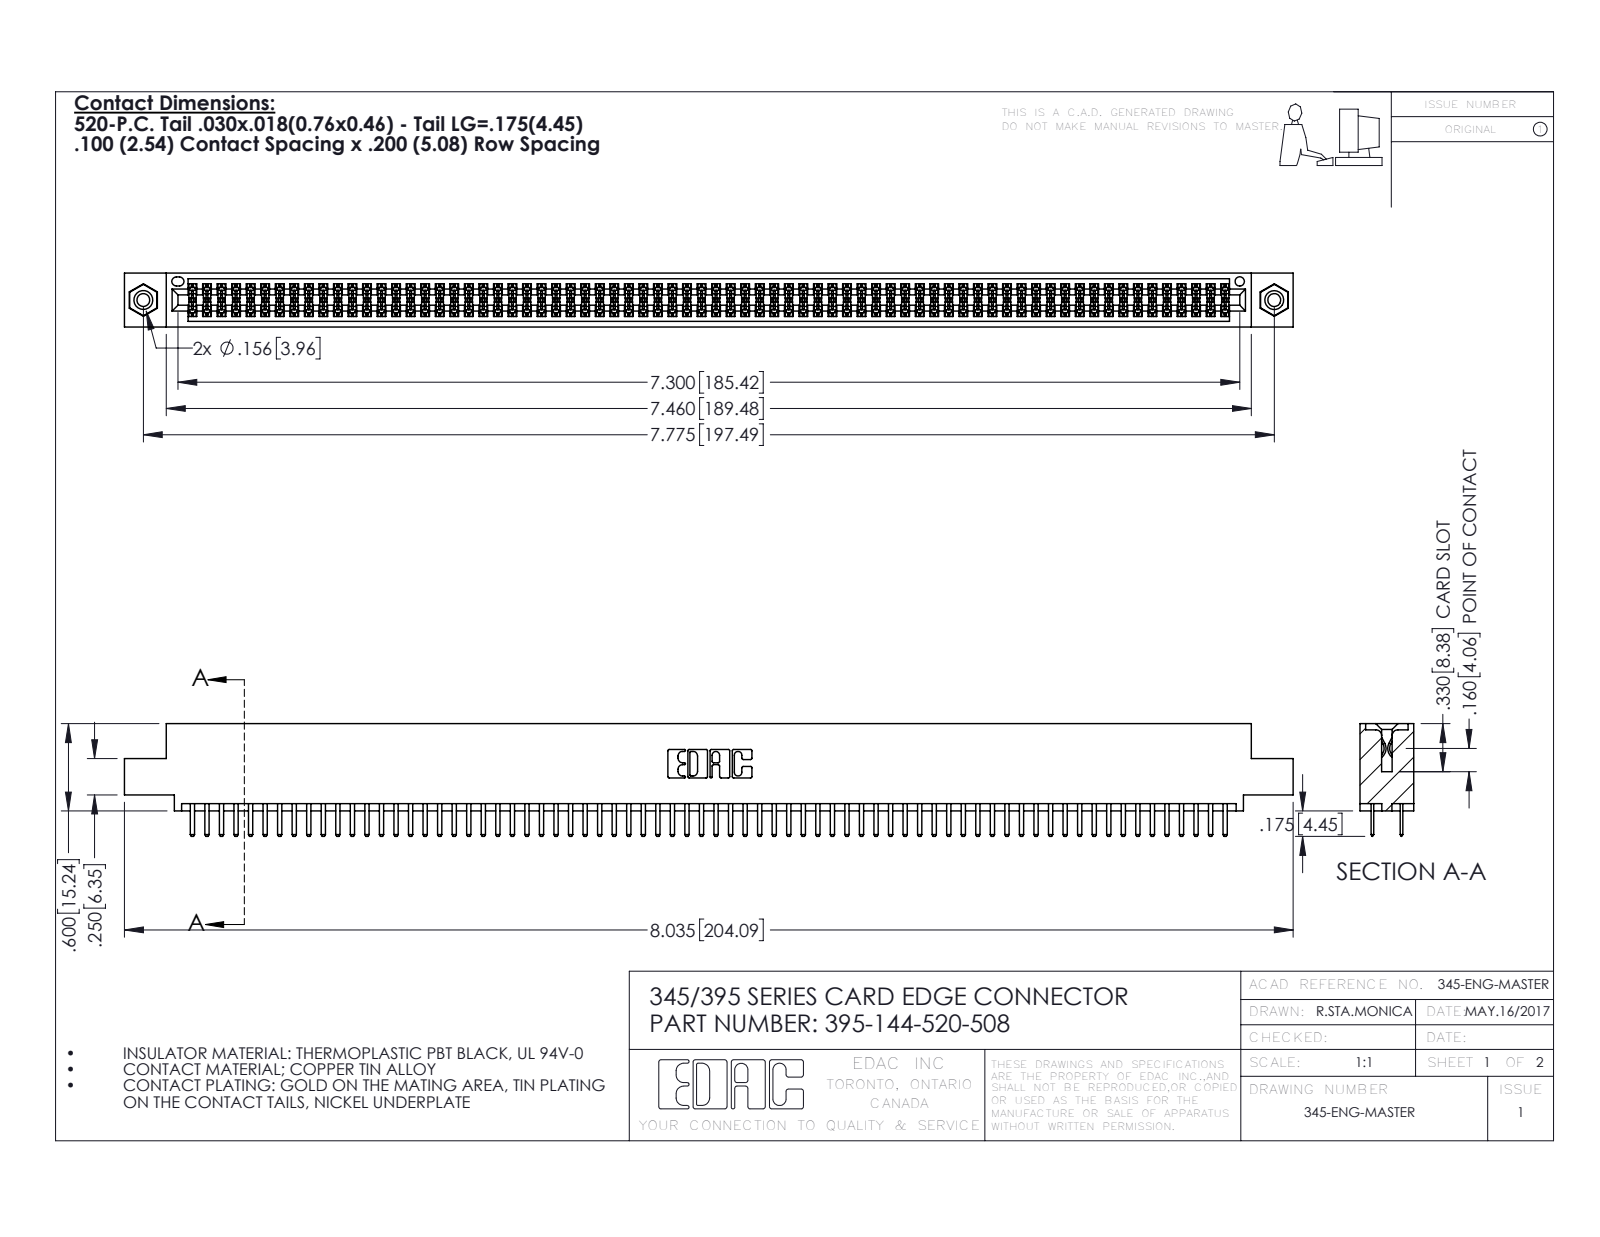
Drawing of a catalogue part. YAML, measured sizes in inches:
part_name: "345 Part_0.110 Offset - 0.156 Dia-TI; 345-250-001_345-250-003-102; 345-292-001_345-293-120; 395-144-520-508"
step_written_by: "SolidWorks 2016 (CONFIG_CONTROL_DESIGN)"
units: inches
bodies: {solids: 147, faces: 7966, planar: 5156, cylindrical: 2794, other: 16}
overall_size: [8.035, 0.775, 0.37]
volume: 1.218
surface_area: 46.59
round_holes:
  - {diameter: 0.089, count: 2}
  - {diameter: 0.125, count: 2}
  - {diameter: 0.156, count: 2}
  - {diameter: 0.064, count: 1}
round_bosses_or_shafts:
  - {diameter: 0.155, count: 2}
partial_cylinders:
  - {radius: 0.006, count: 216}
  - {radius: 0.01, count: 148}
  - {radius: 0.01, count: 22}
  - {radius: 0.007, count: 6}
  - {radius: 0.031, count: 6}
  - {radius: 0.026, count: 3}
  - {radius: 0.014, count: 2}
  - {radius: 0.019, count: 2}
face_to_face_distances: [0.072, 0.298, 0.2, 0.37, 0.098, 0.272, 0.025, 0.225, 0.022, 0.072]
hole_center_spacings: [0.27, 7.539, 7.775]
